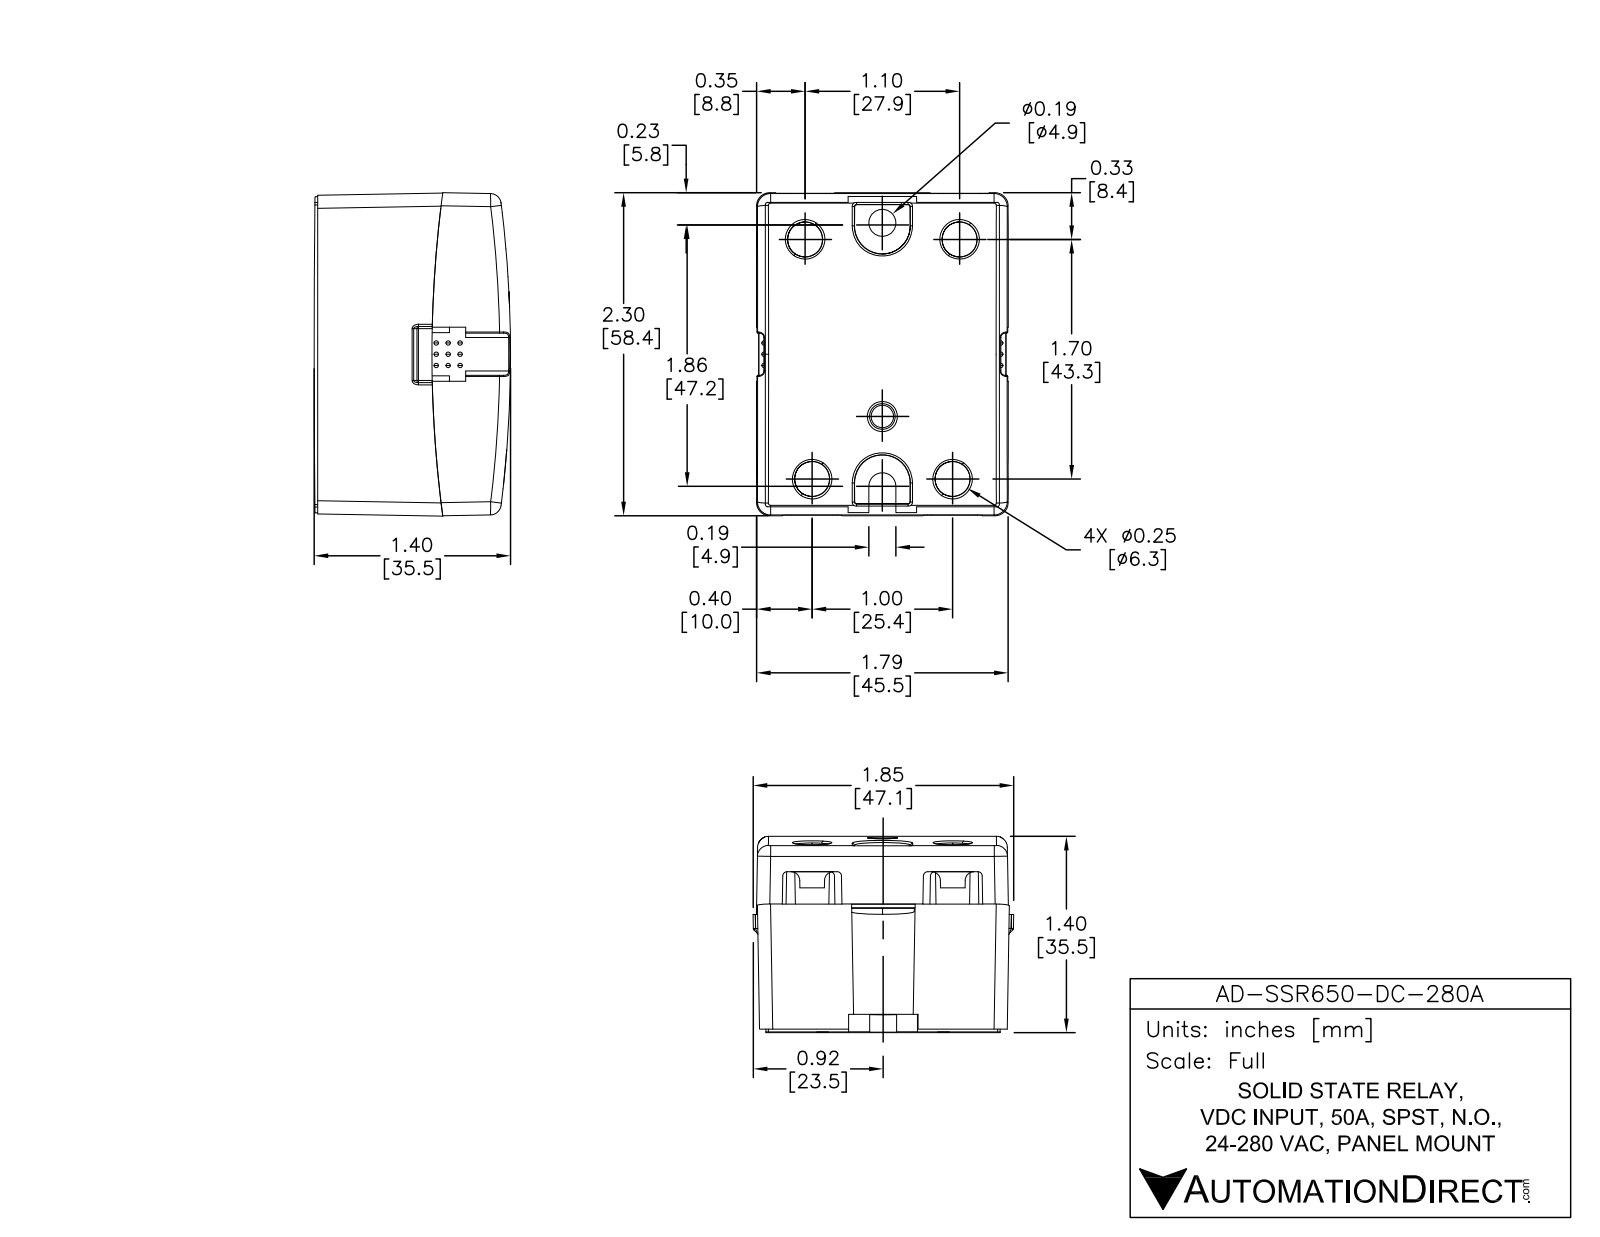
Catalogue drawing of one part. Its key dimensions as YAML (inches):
part_name: "AD-SSR650-DC-280A"
step_written_by: "SolidWorks 2013 (AUTOMOTIVE_DESIGN)"
units: inches
bodies: {solids: 3, faces: 251, planar: 145, cylindrical: 95, other: 11}
overall_size: [2.3, 1.79, 1.4]
volume: 5.14
surface_area: 26.41
round_holes:
  - {diameter: 0.25, count: 4}
  - {diameter: 0.19, count: 1}
round_bosses_or_shafts:
  - {diameter: 0.4, count: 2}
  - {diameter: 0.35, count: 2}
  - {diameter: 0.3, count: 2}
  - {diameter: 0.25, count: 2}
  - {diameter: 0.2, count: 2}
  - {diameter: 0.2, count: 2}
partial_cylinders:
  - {radius: 0.03, count: 6}
  - {radius: 0.01, count: 4}
  - {radius: 0.04, count: 4}
  - {radius: 0.5, count: 4}
  - {radius: 0.194, count: 2}
  - {radius: 0.095, count: 1}
  - {radius: 0.5, count: 1}
  - {radius: 0.5, count: 1}
face_to_face_distances: [1.79, 2.3, 1.166, 0.25, 0.916, 0.671, 1.059, 0.5, 1.8, 0.08]
hole_center_spacings: [0.556, 0.565, 1, 1.1, 1.7, 1.701, 1.876, 1.879]
